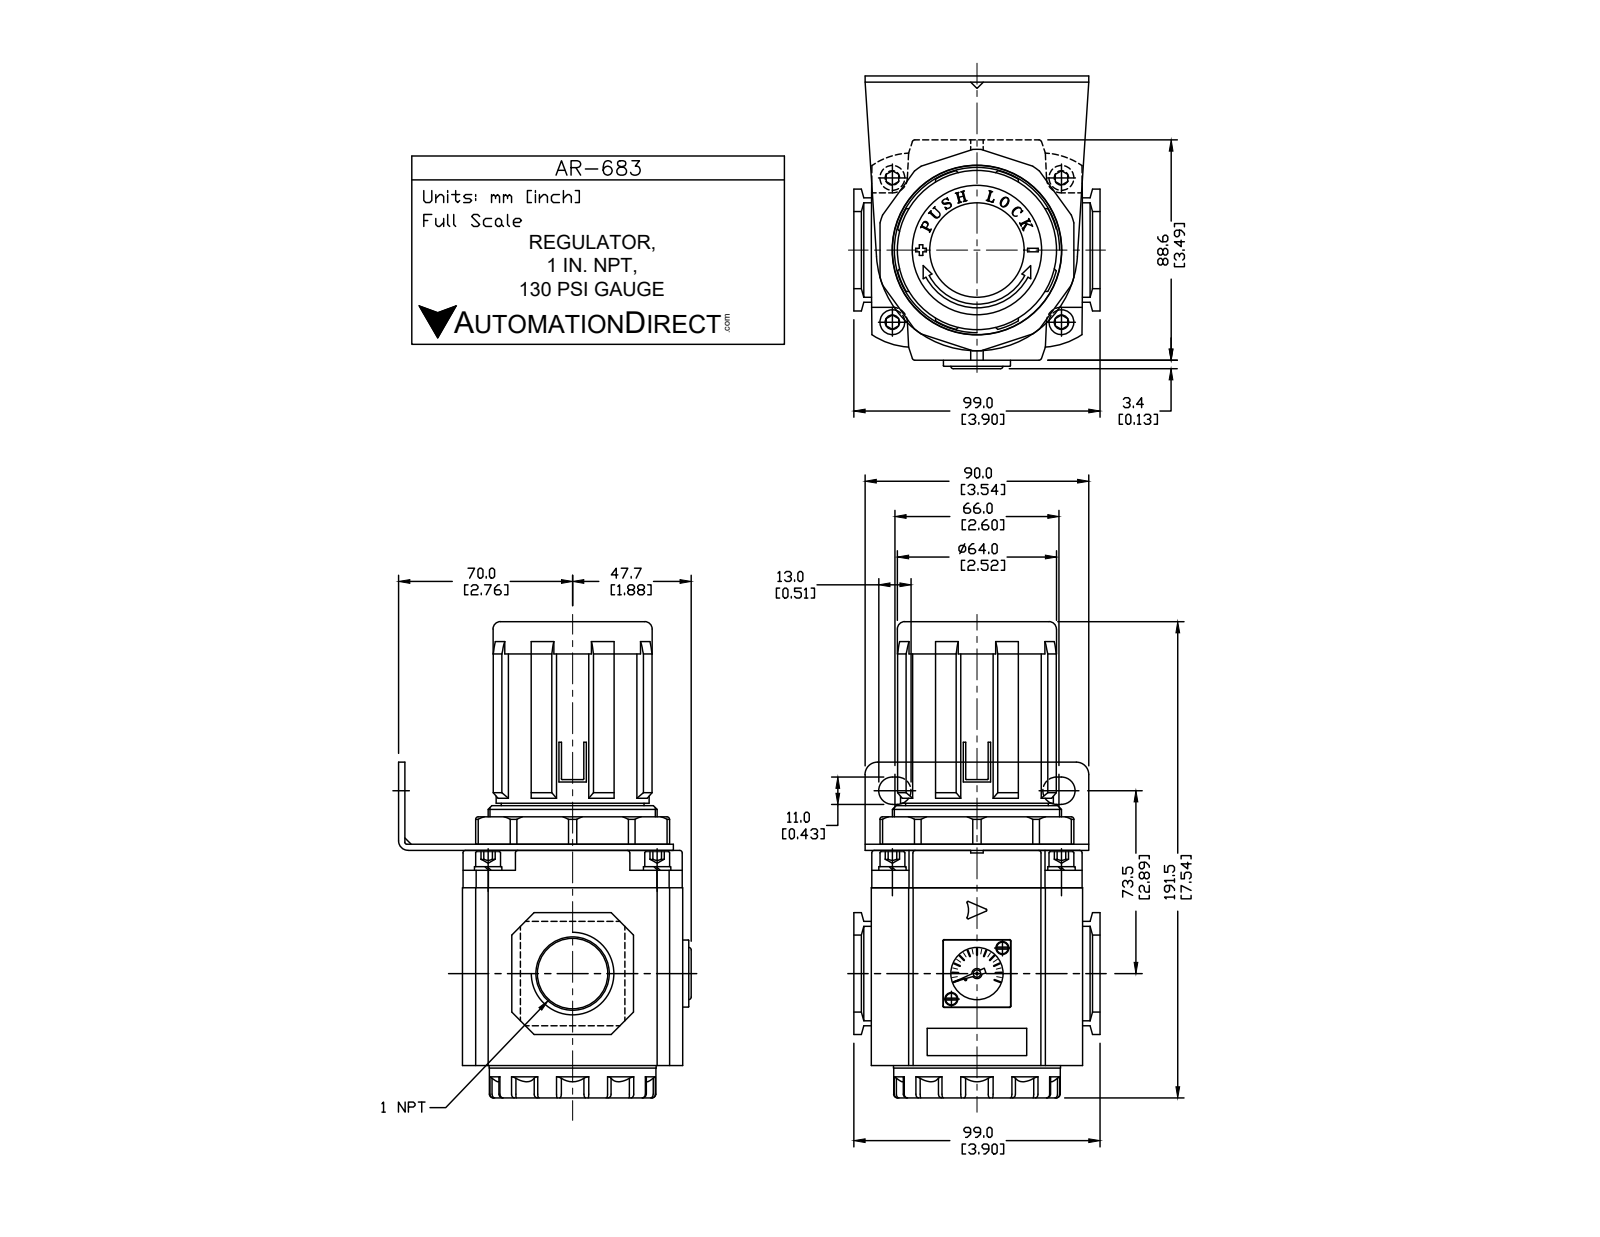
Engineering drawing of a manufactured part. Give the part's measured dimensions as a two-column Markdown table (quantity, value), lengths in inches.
| quantity | value |
| --- | --- |
| part name | AR-683 |
| STEP written by | SolidWorks 2015 (CONFIG_CONTROL_DESIGN) |
| units | inches |
| bodies | 11 solids, 475 faces (326 planar, 111 cylindrical, 38 other) |
| overall size | 7.539 × 4.606 × 3.898 |
| volume | 60.97 in³ |
| surface area | 189.7 in² |
| round holes (diameter × count) | 0.118 × 4, 0.079 × 1, 0.709 × 1, 1.141 × 1, 1.181 × 1 |
| round bosses / shafts (diameter × count) | 0.394 × 4, 2.677 × 1, 2.638 × 1, 2.585 × 1, 2.52 × 1, 2.117 × 1, 0.157 × 1, 0.031 × 1 |
| partial cylindrical surfaces (radius × count) | 0.047 × 10, 0.012 × 4, 0.039 × 4, 0.217 × 4, 0.276 × 4, 0.783 × 4, 0.008 × 3, 0.128 × 2 |
| main face-to-face distances | 0.098, 3.504, 3.406, 3.622, 3.488, 3.917, 3.346, 0.276, 0.512, 4.016 |
| hole center spacings | 1.628, 2.093, 2.494, 3.256 |
